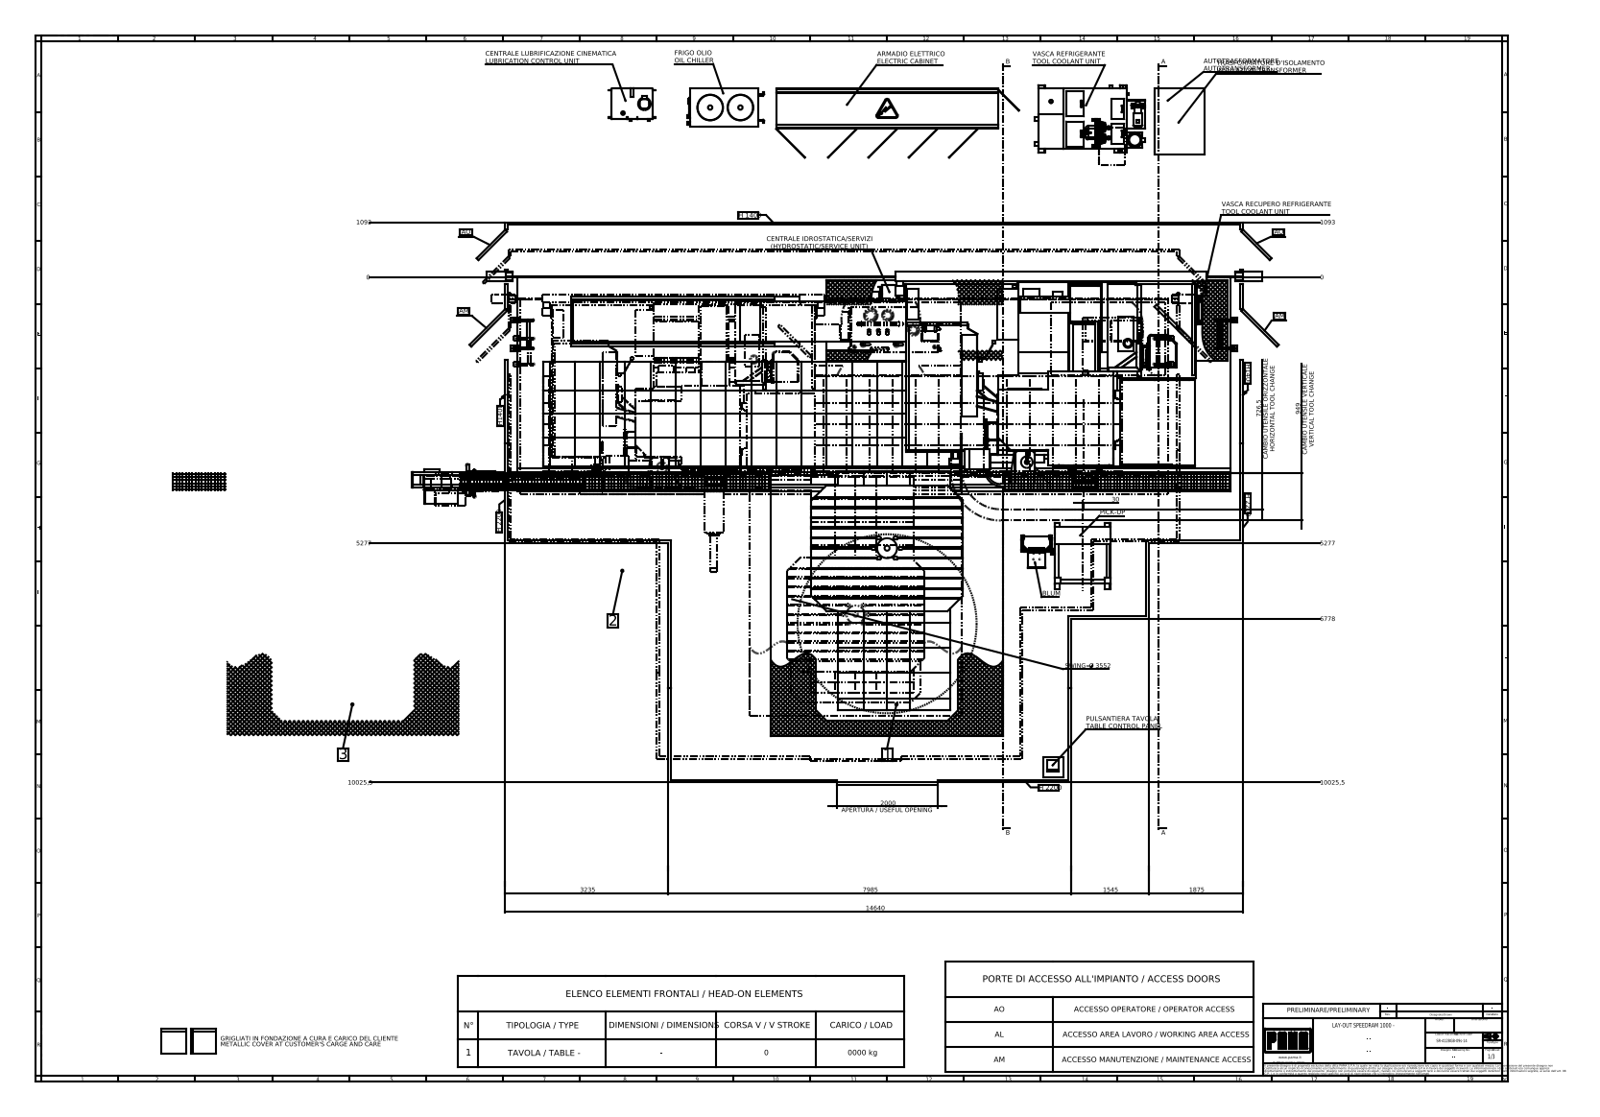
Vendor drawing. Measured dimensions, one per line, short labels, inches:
name: S001774_2500x3000 (PASSO CAVA = 200) SM. 300x300; S003304; S001573; LAYOUT SPEEDRAM PMS V2.0 (+8 more)
written by: SolidWorks 2023 (AUTOMOTIVE_DESIGN)
unit: in
bodies: 507 solids, 8183 faces (5588 planar, 2101 cylindrical, 494 other)
size: 714.173 × 661.02 × 388.051
volume: 33 370 000 in³; area: 3 182 000 in²
holes: 183× ⌀2.74, 108× ⌀1.378, 18× ⌀1.465, 9× ⌀1.181, 8× ⌀0.512, 8× ⌀0.551, 6× ⌀0.315, 5× ⌀13.386, 4× ⌀0.492, 4× ⌀2.231, 4× ⌀2.362, 3× ⌀1.008
bosses: 18× ⌀1.669, 14× ⌀0.787, 11× ⌀1.575, 10× ⌀5.906, 10× ⌀0.354, 9× ⌀2.362, 8× ⌀2.165, 7× ⌀2.61
rounds: 192× R0.197, 93× R0.591, 62× R1.378, 52× R0.315, 28× R0.236, 28× R0.394, 26× R0.787, 23× R0.118
face distances: 78.74, 1.969, 29.646, 49.094, 0.394, 658.209, 714.173, 435.768, 0.197, 41.063
hole spacings: 10.753, 19.685, 48.644, 29.843, 56.047, 39.37, 49.403, 68.493
